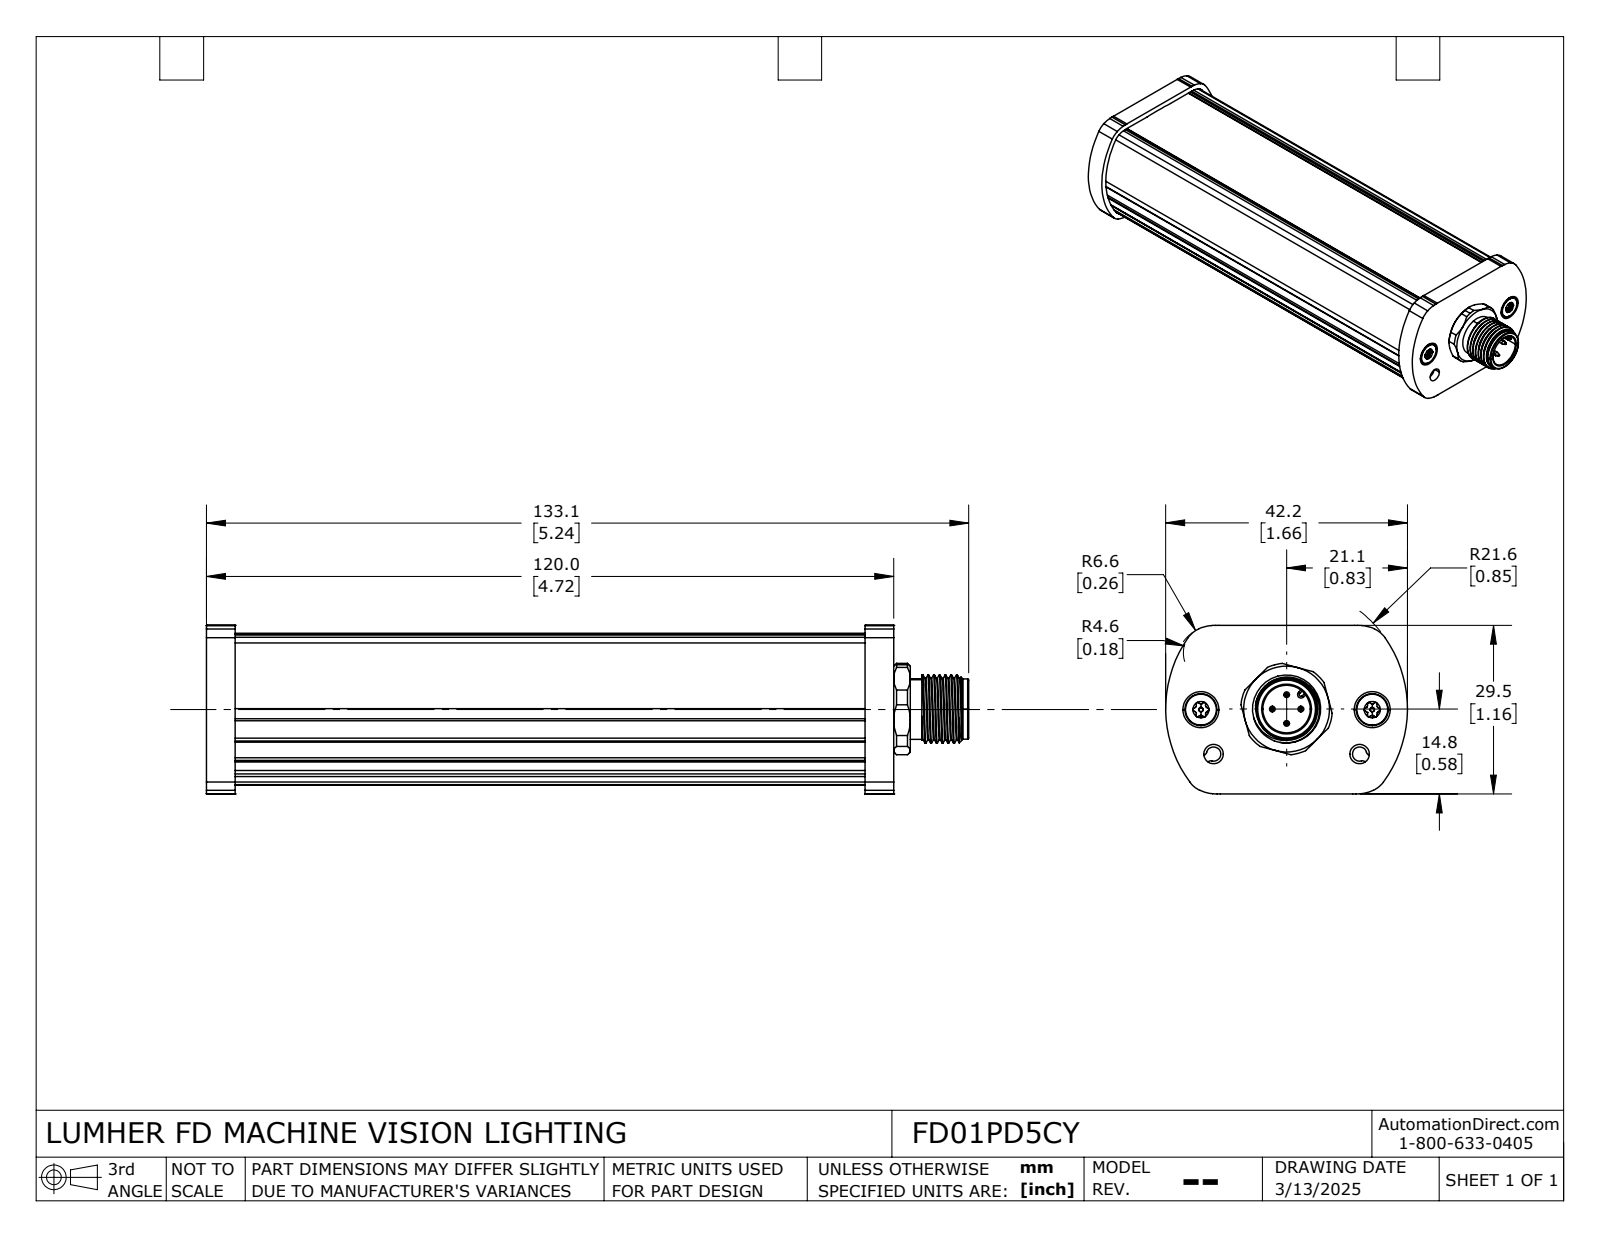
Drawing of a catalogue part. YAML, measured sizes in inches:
part_name: "FD01PD5CY"
step_written_by: "SolidWorks 2024 (AUTOMOTIVE_DESIGN)"
units: inches
bodies: {solids: 1, faces: 662, planar: 97, cylindrical: 383, other: 182}
overall_size: [5.24, 1.662, 1.159]
volume: 6.304
surface_area: 49.07
round_holes:
  - {diameter: 0.057, count: 4}
  - {diameter: 0.134, count: 4}
  - {diameter: 0.327, count: 1}
  - {diameter: 0.354, count: 1}
  - {diameter: 0.37, count: 1}
round_bosses_or_shafts:
  - {diameter: 0.055, count: 4}
  - {diameter: 0.039, count: 4}
  - {diameter: 0.22, count: 2}
  - {diameter: 0.118, count: 2}
  - {diameter: 0.031, count: 2}
  - {diameter: 0.469, count: 1}
  - {diameter: 0.417, count: 1}
  - {diameter: 0.413, count: 1}
partial_cylinders:
  - {radius: 0.022, count: 24}
  - {radius: 0.01, count: 12}
  - {radius: 0.031, count: 12}
  - {radius: 0.118, count: 10}
  - {radius: 0.012, count: 4}
  - {radius: 0.049, count: 4}
  - {radius: 0.122, count: 4}
  - {radius: 0.181, count: 4}
face_to_face_distances: [0.098, 0.197, 0.295, 0.079, 0.118, 0.394, 4.528, 4.646, 0.039, 4.606]
hole_center_spacings: [0.098, 0.139, 0.589, 0.197, 0.317, 0.491, 0.508, 0.544]
